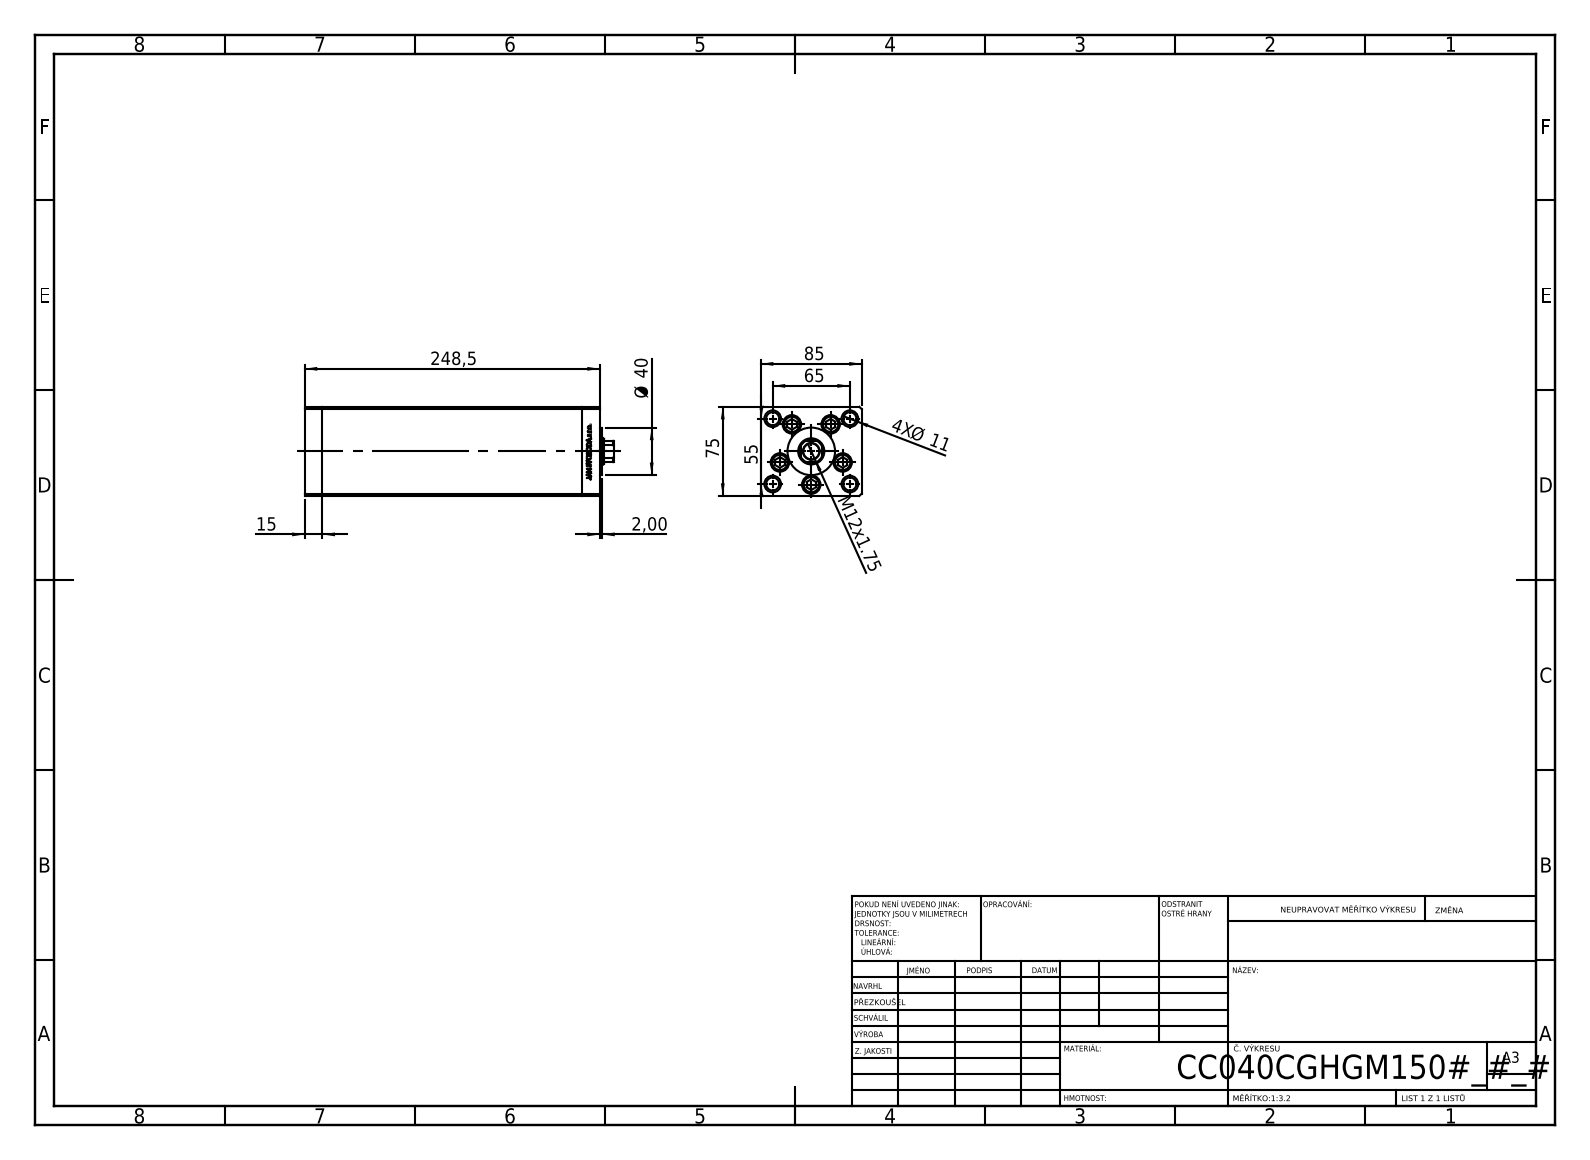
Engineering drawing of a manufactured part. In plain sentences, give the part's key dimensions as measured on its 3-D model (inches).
The part is named "V220C FRONT; V220C_VC_C; V220C_C MIDDLE; ALLEN BOLT (+1 more)". Its 3-D file was written by "SolidWorks 2019 (CONFIG_CONTROL_DESIGN)". It is 13 solids with 1185 faces: 548 planar, 175 cylindrical and 462 other. Overall it measures 10.236 by 3.346 by 2.953 inches. Its volume is 79.76 cubic inches and its surface area 344.2 square inches. Round holes: 9 of diameter 0.433, 5 of diameter 0.61, 4 of diameter 0.079, 4 of diameter 0.394, 4 of diameter 0.518, 4 of diameter 0.551, 1 of diameter 0.531, 1 of diameter 0.571, 1 of diameter 0.866. Round bosses or shafts: 5 of diameter 0.315, 4 of diameter 0.571, 1 of diameter 1.575. Partial cylindrical surfaces (rounded edges, fillets, slot ends): 2 of radius 0.037, 1 of radius 0.413. The main face-to-face distances are 3.346, 2.953, 0.591, 8.602, 9.193, 0.413, 9.783, 1.348, 2.697, 2.539. The hole center spacings are 1.102, 1.676, 0.664, 0.755, 1.273, 1.28, 1.324, 1.47.
